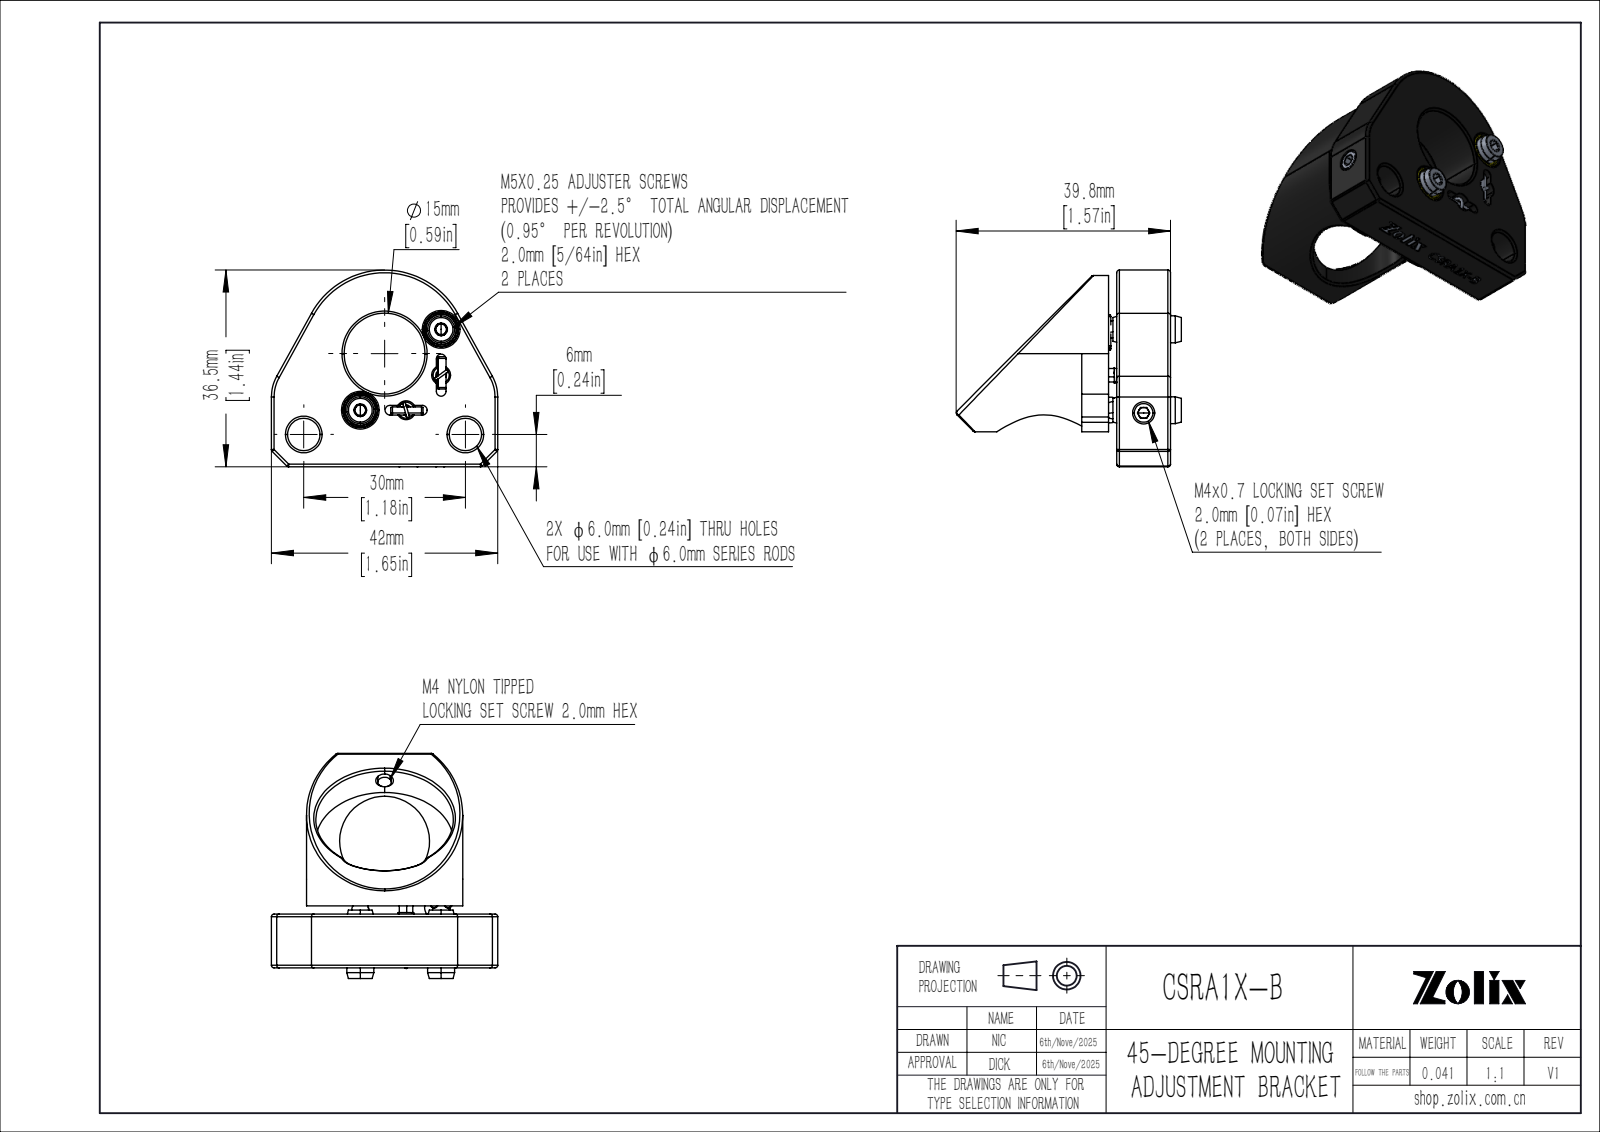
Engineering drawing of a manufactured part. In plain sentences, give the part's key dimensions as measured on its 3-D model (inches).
The part is named "CSRA1X-B". Its 3-D file was written by "SolidWorks 2020 (CONFIG_CONTROL_DESIGN)". It is 20 solids with 756 faces: 382 planar, 128 cylindrical and 246 other. Overall it measures 1.654 by 1.644 by 1.437 inches. Its volume is 0.934 cubic inches and its surface area 16.39 square inches. Round holes: 3 of diameter 0.236, 2 of diameter 0.077, 2 of diameter 0.081, 2 of diameter 0.13, 2 of diameter 0.138, 2 of diameter 0.197, 2 of diameter 0.252, 2 of diameter 0.283, 1 of diameter 0.118, 1 of diameter 0.125, 1 of diameter 0.125, 1 of diameter 0.126. Round bosses or shafts: 4 of diameter 0.059, 3 of diameter 0.098, 2 of diameter 0.28, 2 of diameter 0.157, 1 of diameter 1.142, 1 of diameter 0.236. Partial cylindrical surfaces (rounded edges, fillets, slot ends): 19 of radius 0.02, 4 of radius 0.03, 4 of radius 0.035, 4 of radius 0.236, 2 of radius 0.134, 2 of radius 0.315, 1 of radius 0.502, 1 of radius 0.528. The main face-to-face distances are 0.394, 0.059, 0.453, 0.256, 0.236, 1.654, 0.197, 1.398, 0.65, 0.02. The hole center spacings are 0.45, 0.835, 0.335, 0.443, 0.468, 0.644, 0.788, 0.362.
